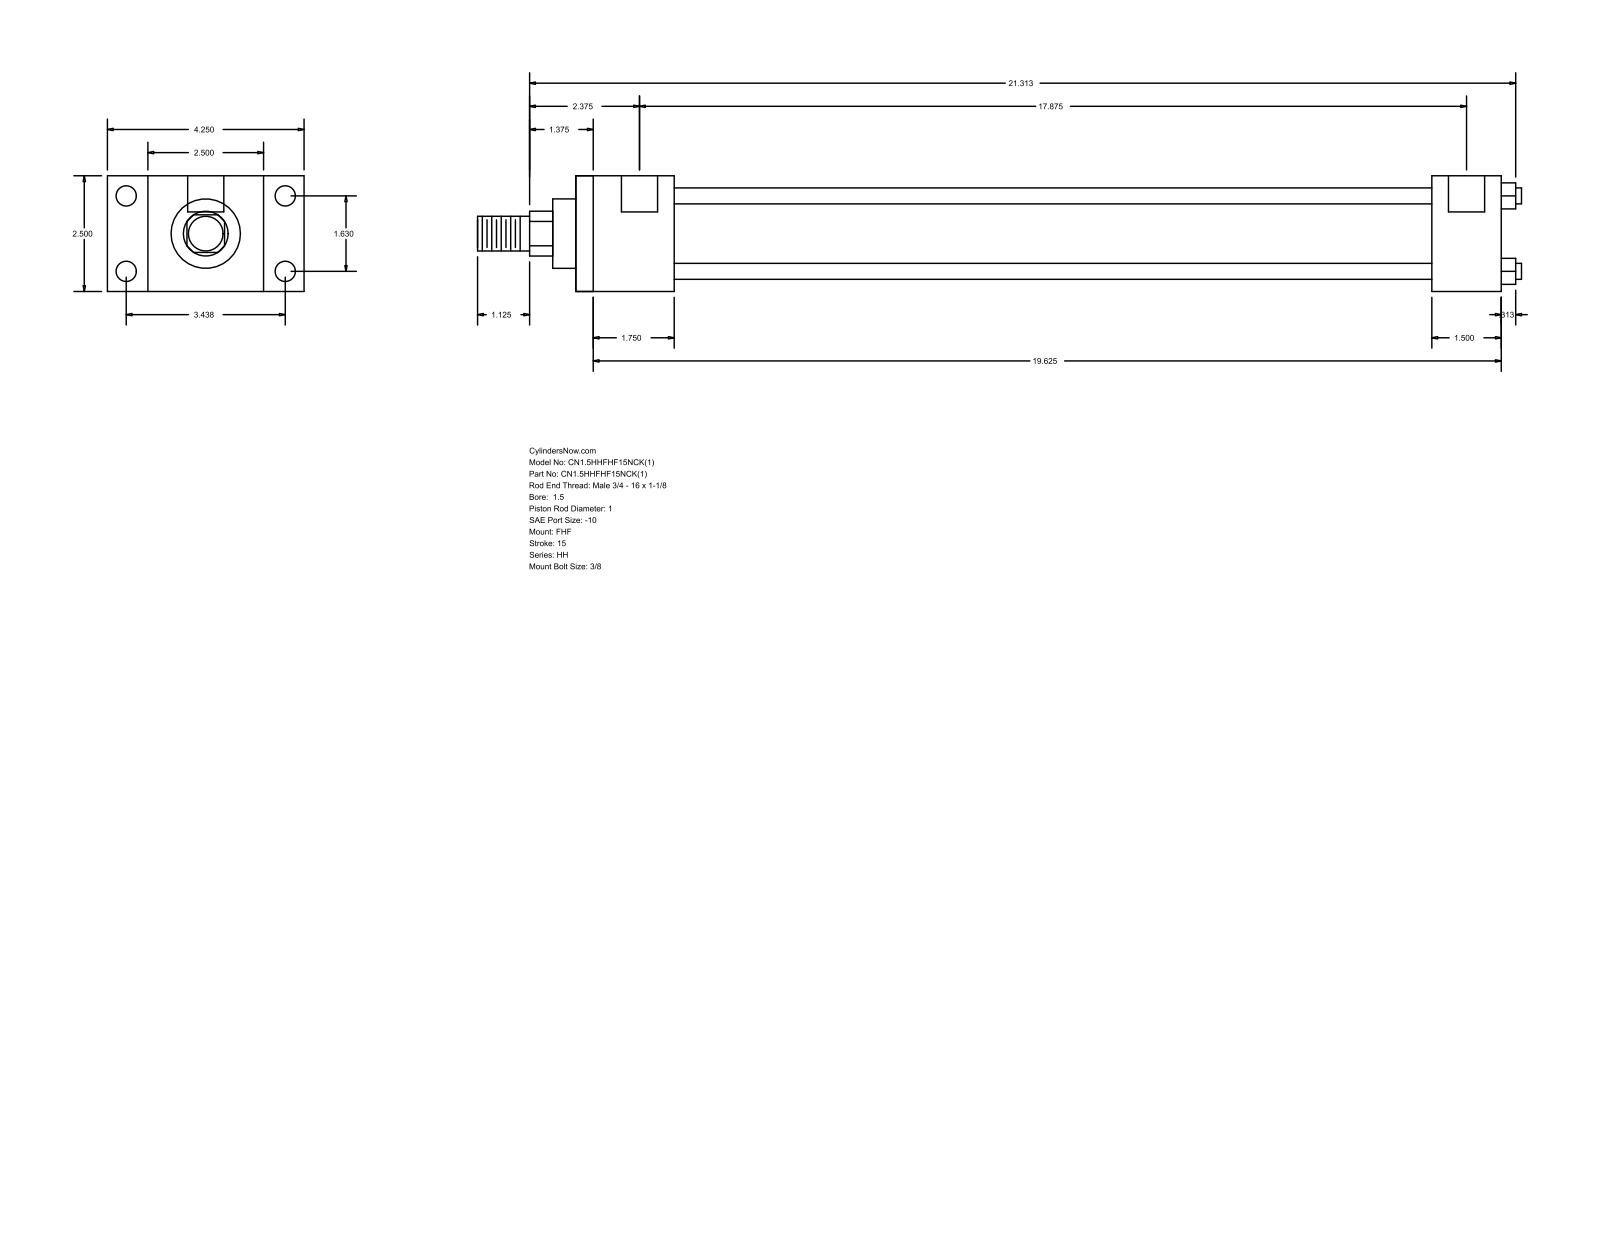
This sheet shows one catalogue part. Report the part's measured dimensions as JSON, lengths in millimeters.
{"part_name": "HH_FHF__0150_1", "step_written_by": "GSSL Pune (CONFIG_CONTROL_DESIGN)", "units": "millimeters", "bodies": {"solids": 0, "faces": 88, "planar": 60, "cylindrical": 28, "other": 0}, "overall_size": [573.09, 107.95, 63.5], "round_holes": [[5.56, 4], [11.13, 4], [19.84, 2]], "round_bosses_or_shafts": [[8.76, 4], [44.45, 1], [38.1, 1], [25.4, 1], [19.05, 1]], "partial_cylinders_radius": [[12.29, 1]], "face_to_face_distances": [63.5, 22.23, 85.73, 53.98, 107.96, 508, 454.02, 38.1, 469.9, 415.92], "hole_center_spacings": [1.59, 41.4, 87.32, 96.64, 455.61, 457.2, 454.02]}
